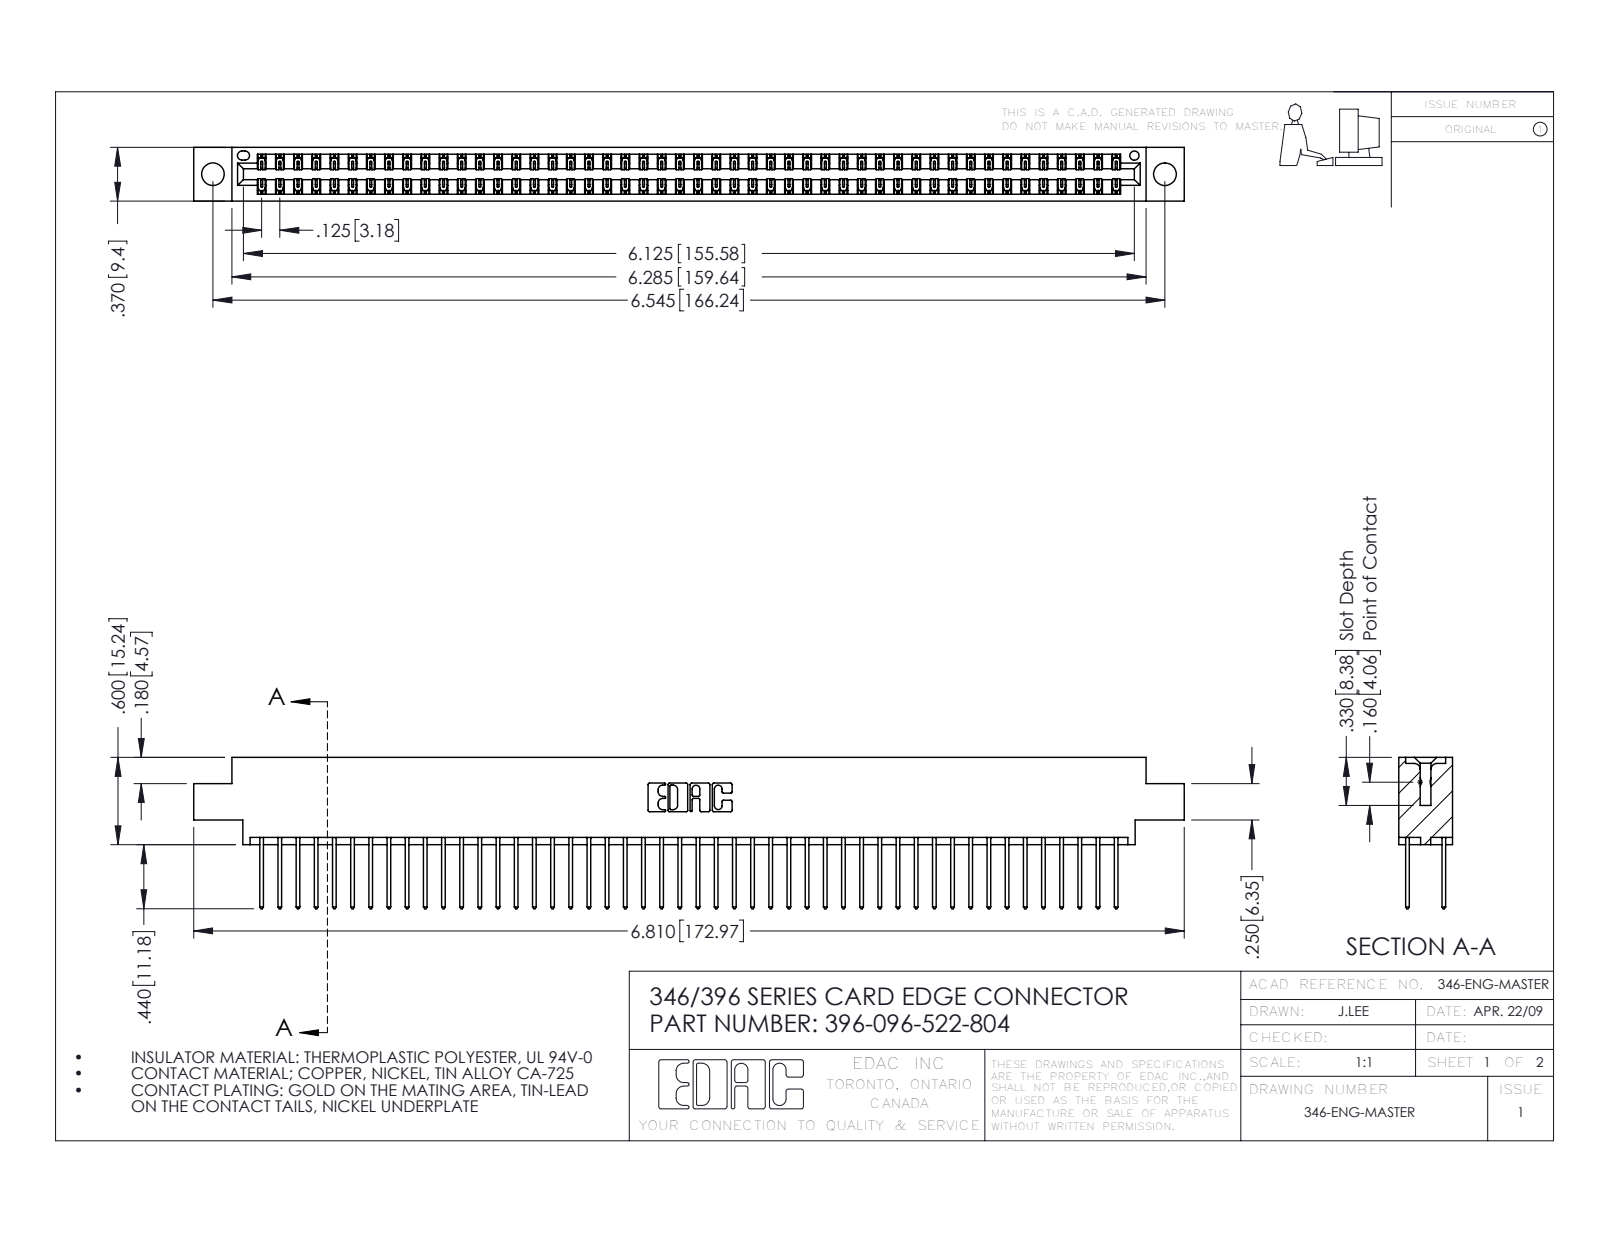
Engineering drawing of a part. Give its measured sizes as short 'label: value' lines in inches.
name: 346 Part_0.170 Offset - 0.156 Dia-TH; 396-096-522-804; 345-292-001_345-293-122
written by: SolidWorks 2016 (CONFIG_CONTROL_DESIGN)
unit: in
bodies: 97 solids, 5118 faces (3440 planar, 1678 cylindrical, 0 other)
size: 6.81 × 1.04 × 0.37
volume: 1.032 in³; area: 37.95 in²
holes: 2× ⌀0.156, 1× ⌀0.064
rounds: 144× R0.006, 96× R0.01, 22× R0.01, 6× R0.007, 6× R0.031, 3× R0.026, 2× R0.014, 2× R0.022
face distances: 0.048, 0.322, 0.25, 0.37, 0.072, 0.298, 0.025, 0.275, 0.148, 0.222
hole spacings: 0.246, 6.336, 6.545
